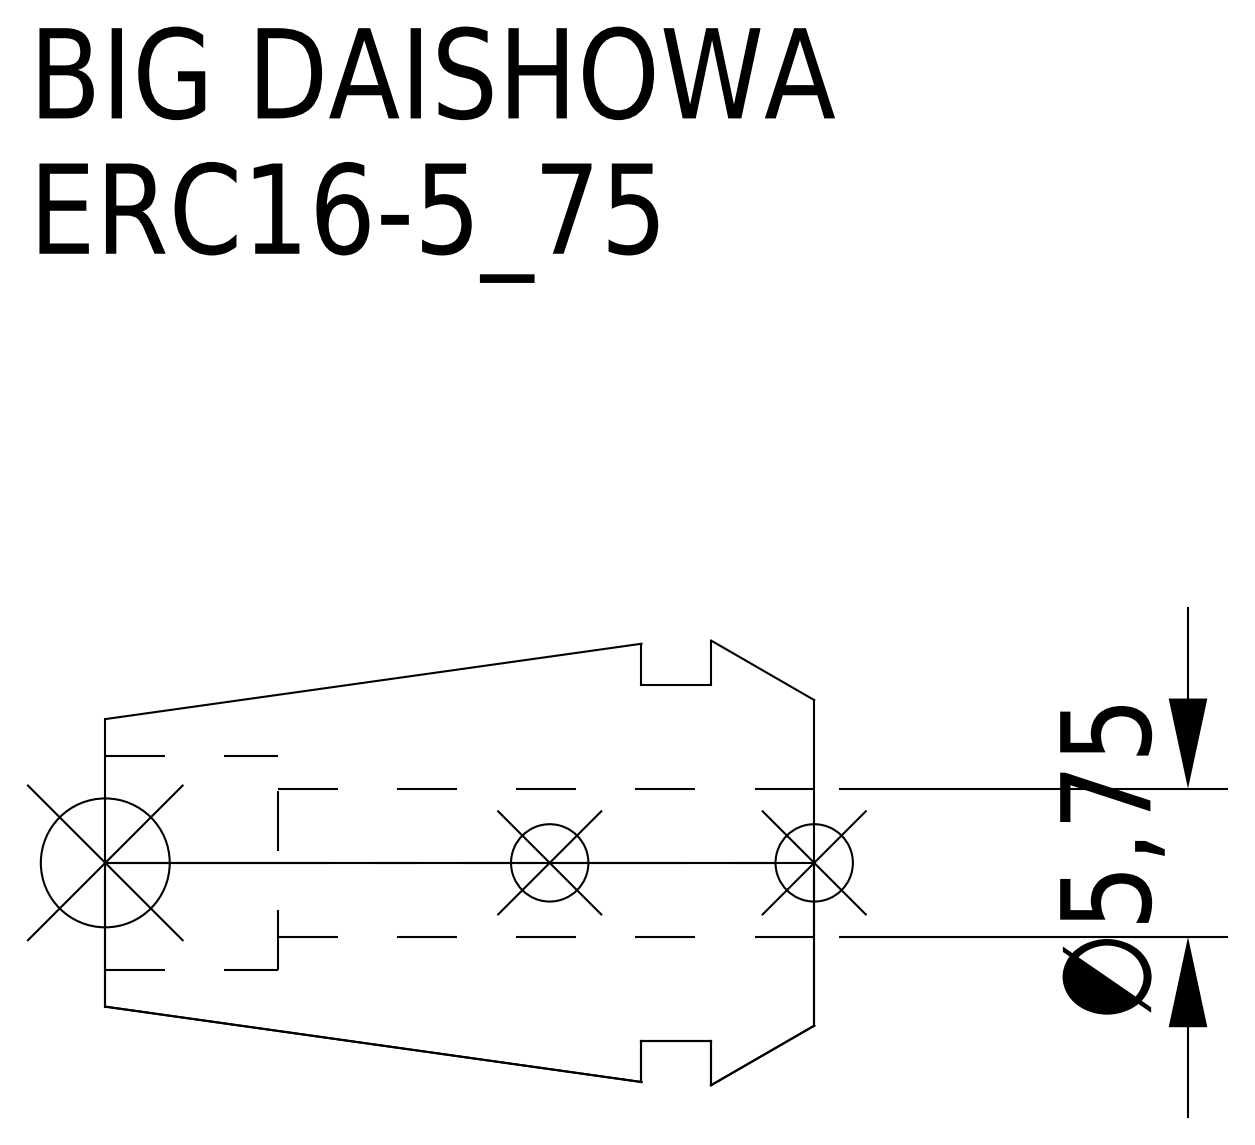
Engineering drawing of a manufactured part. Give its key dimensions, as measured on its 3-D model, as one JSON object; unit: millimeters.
{"part_name": "ERC16-5_75", "step_written_by": "CREO PARAMETRIC BY PTC INC, 2016380 (AUTOMOTIVE_DESIGN)", "units": "millimeters", "bodies": {"solids": 1, "faces": 15, "planar": 5, "cylindrical": 6, "other": 4}, "overall_size": [27.5, 17.25, 17.25], "volume_mm3": 3492, "surface_area_mm2": 2146, "round_holes": [[5.75, 1], [8.3, 1]], "round_bosses_or_shafts": [[13.8, 1]], "face_to_face_distances": [4, 6.7, 2.7, 27.5, 23.5, 20.8, 20.79, 16.79, 14.09, 6.71]}
